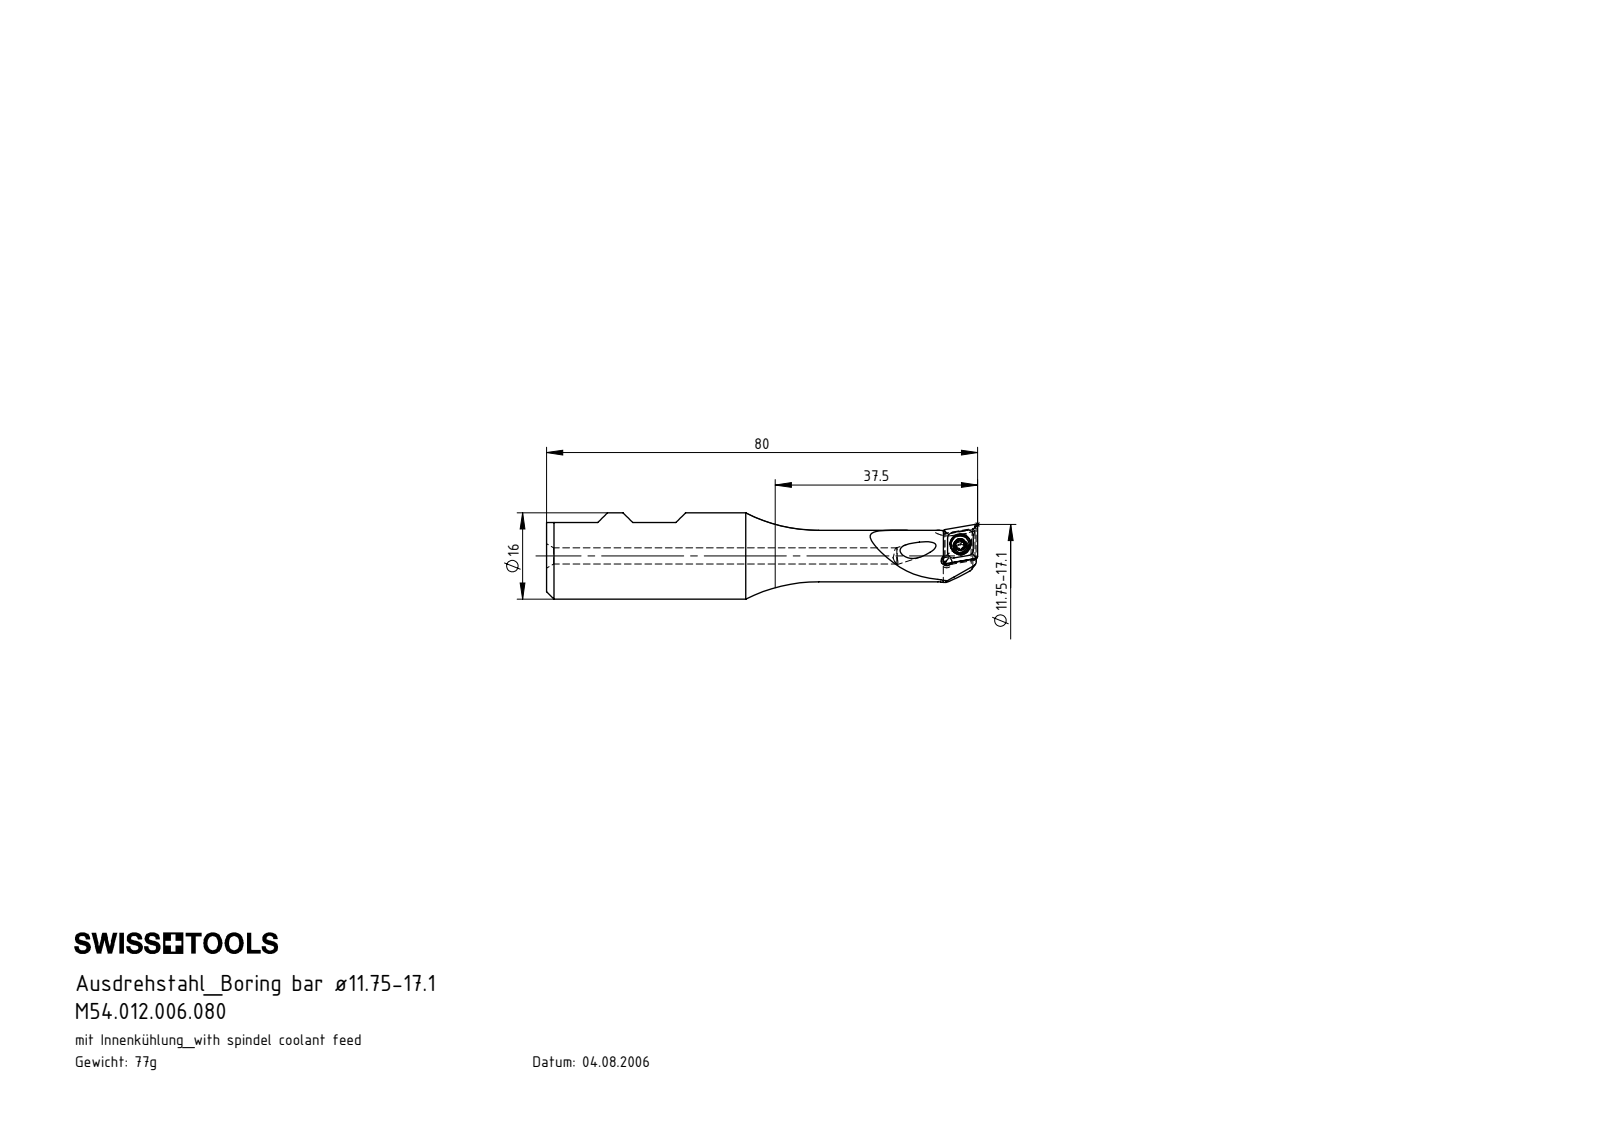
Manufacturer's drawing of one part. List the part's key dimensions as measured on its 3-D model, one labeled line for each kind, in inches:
Part name (STEP PRODUCT): WCA-ER2.001.005_A; CCMT060204; B12-WCA.K11.080_B; B12.WCA.K11.080
STEP written by: SolidWorks 2017 (AUTOMOTIVE_DESIGN)
Units: inches
Bodies: 3 solids, 105 faces (36 planar, 28 cylindrical, 41 other)
Overall size (bounding box): 3.15 × 0.63 × 0.63
Volume: 0.599 in³ · Surface area: 6.557 in²
Round holes (diameter × count): ⌀0.118 ×2, ⌀0.079 ×1, ⌀0.081 ×1, ⌀0.11 ×1, ⌀0.152 ×1
Round bosses / shafts (diameter × count): ⌀0.63 ×1, ⌀0.376 ×1, ⌀0.134 ×1, ⌀0.098 ×1
Partial cylindrical surfaces — rounded edges, fillets, slot ends (radius × count): R0.008 ×6, R0.014 ×5, R0.014 ×1, R0.039 ×1, R0.157 ×1, R0.193 ×1, R0.276 ×1, R0.315 ×1
Main face-to-face distances: 0.086, 0.404, 0.094, 2.904, 0.139, 0.225, 0.233, 0.198, 0.058, 0.028
Hole centre spacings: 0.153, 0.157
